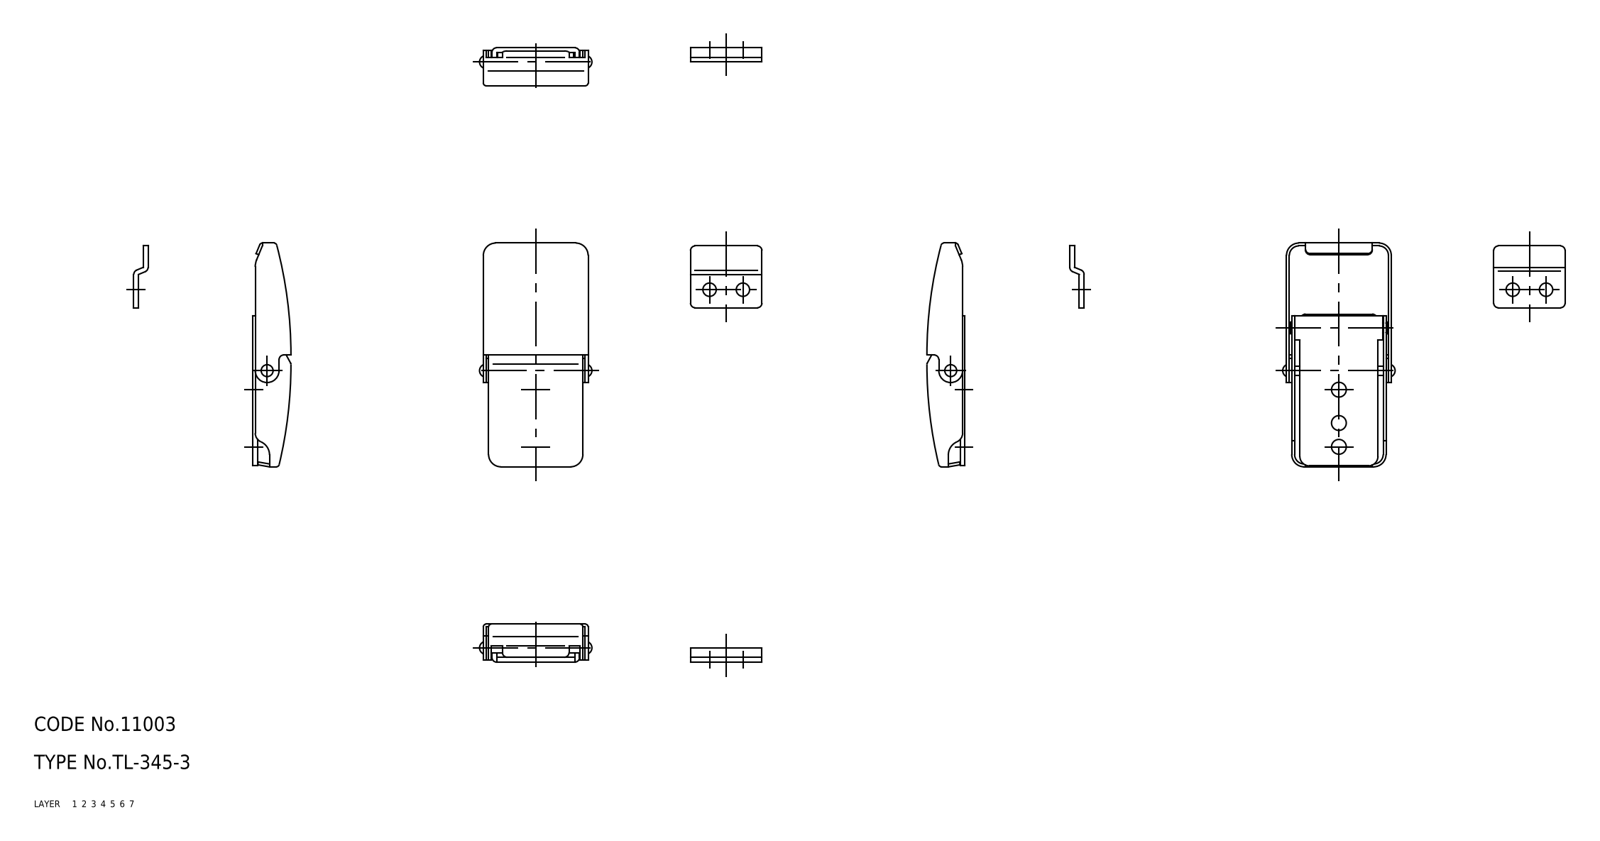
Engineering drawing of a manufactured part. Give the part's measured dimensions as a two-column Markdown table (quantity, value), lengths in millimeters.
| quantity | value |
| --- | --- |
| part name | washer; shaft_B; shaft_A; rivet (+6 more) |
| STEP written by | CADfix (AUTOMOTIVE_DESIGN) |
| units | millimeters |
| bodies | 10 solids, 218 faces (0 planar, 0 cylindrical, 218 other) |
| overall size | 47 × 23.6 × 8 |
| volume | 2 174 mm³ |
| surface area | 6 654 mm² |
